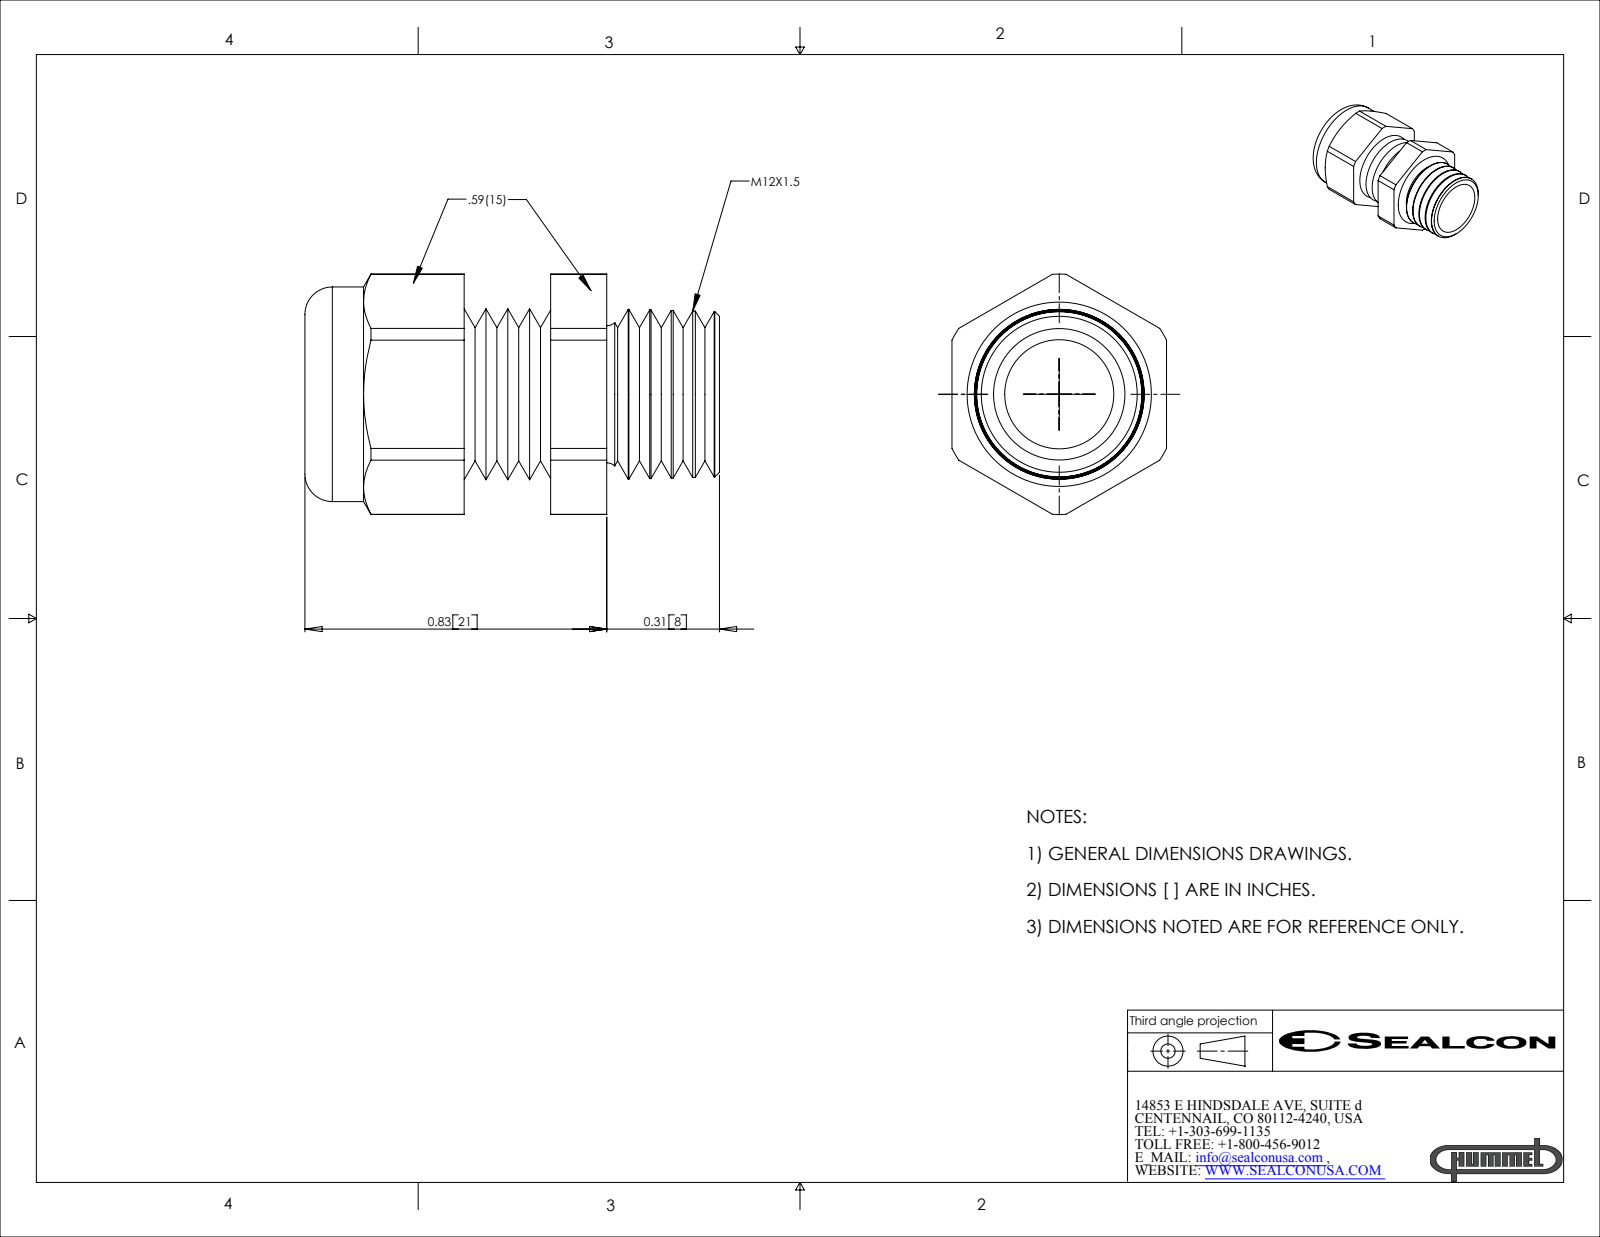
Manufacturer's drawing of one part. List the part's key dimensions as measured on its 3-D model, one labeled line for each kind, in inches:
Part name (STEP PRODUCT): CD12MA-GY
STEP written by: SolidWorks 2007 (CONFIG_CONTROL_DESIGN)
Units: inches
Bodies: 2 solids, 108 faces (20 planar, 24 cylindrical, 64 other)
Overall size (bounding box): 1.14 × 0.661 × 0.59
Volume: 0.151 in³ · Surface area: 4.819 in²
Round holes (diameter × count): ⌀0.3 ×1, ⌀0.4 ×1, ⌀0.47 ×1
Round bosses / shafts (diameter × count): ⌀0.59 ×1
Partial cylindrical surfaces — rounded edges, fillets, slot ends (radius × count): R0.33 ×1
Main face-to-face distances: 0.59, 0.238, 0.277, 0.515, 0.669, 0.392, 0.154, 0.131, 0.408, 0.646
